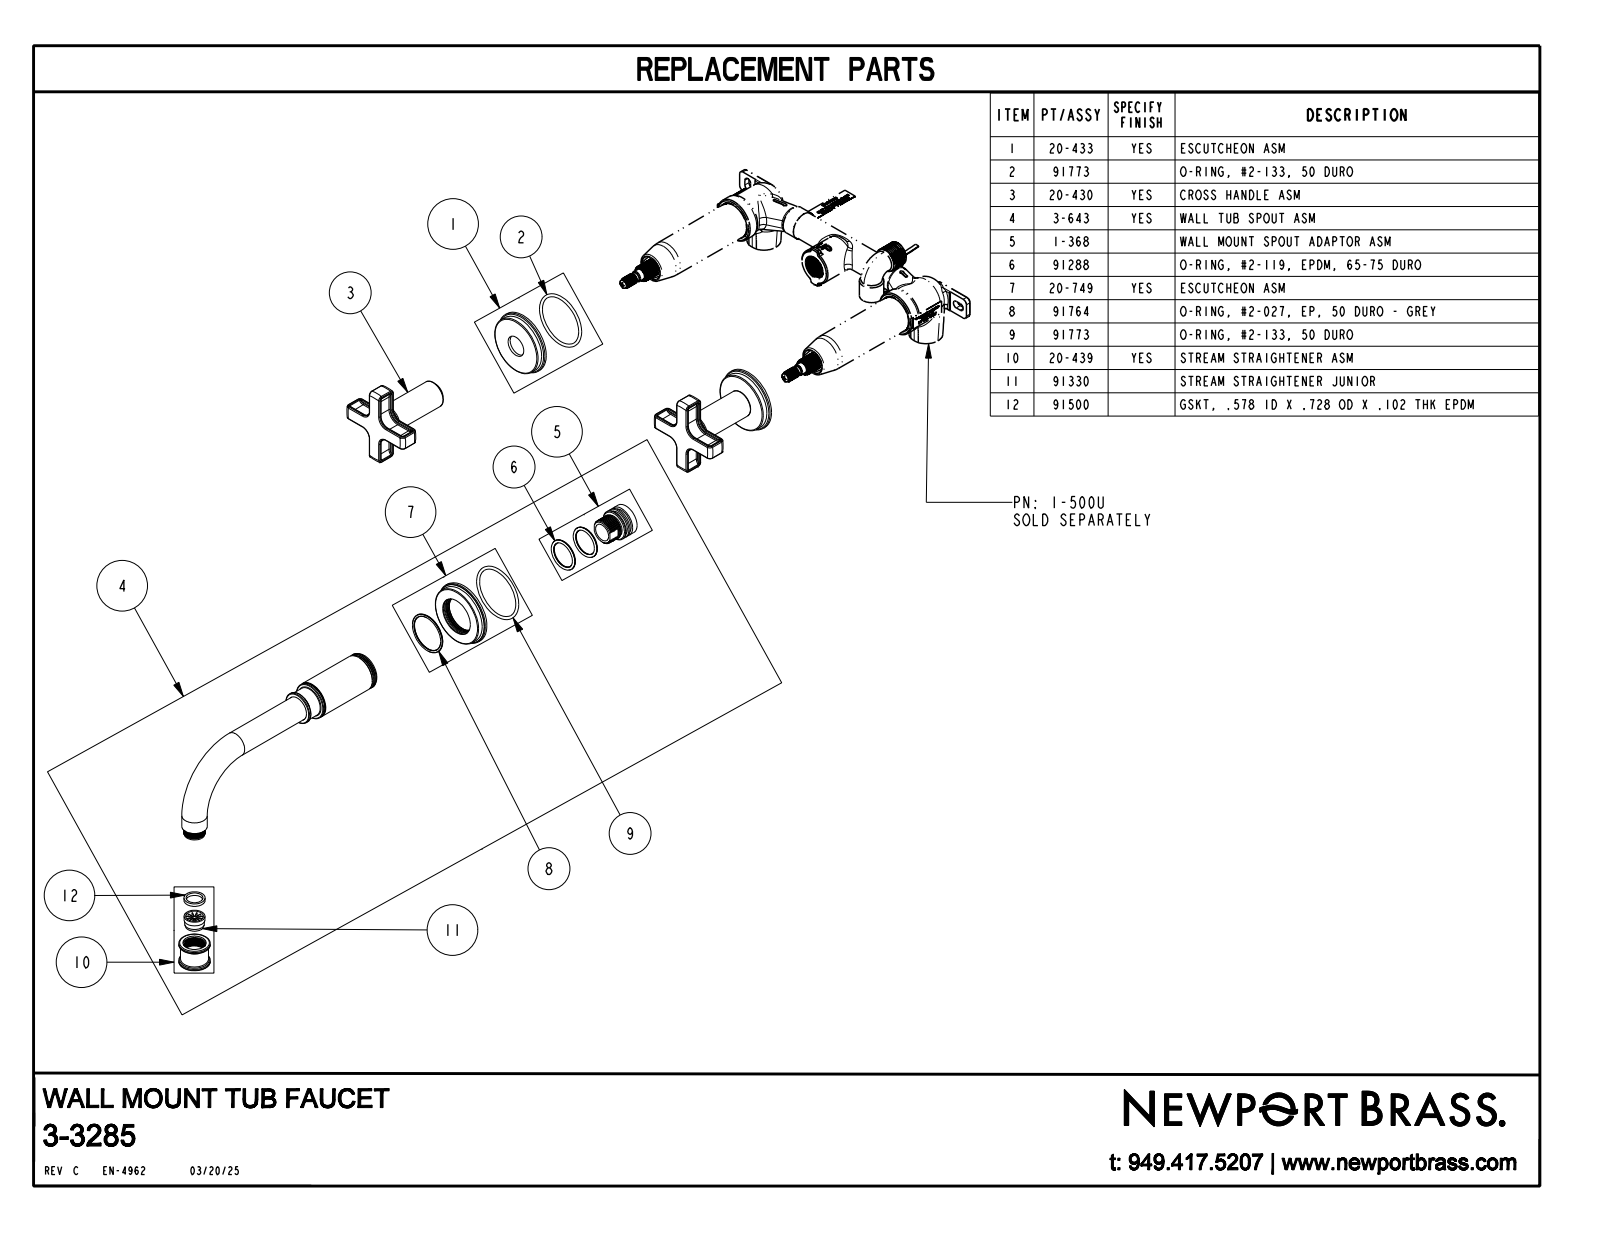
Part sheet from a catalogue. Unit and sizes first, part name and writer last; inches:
Units: inches
Overall size (bounding box): 10.675 × 10.66 × 8.79
Round bosses / shafts (diameter × count): ⌀2.25 ×3, ⌀2.09 ×3, ⌀0.975 ×2, ⌀0.875 ×2, ⌀0.85 ×2, ⌀0.5 ×2, ⌀1.312 ×1, ⌀1.14 ×1
Partial cylindrical surfaces — rounded edges, fillets, slot ends (radius × count): R0.03 ×68, R0.25 ×16, R0.325 ×8, R0.425 ×8, R1.4 ×2
Main face-to-face distances: 0.35, 3.251, 2.901, 2.551, 2.201, 0.7, 0.1, 0.3, 0.6, 0.4
Volume: 18.13 in³ · Surface area: 103.4 in²
Bodies: 3 solids, 508 faces (68 planar, 220 cylindrical, 220 other)
Part name (STEP PRODUCT): 3-3285_SW0001
STEP written by: CREO PARAMETRIC BY PTC INC, 2018400 (AUTOMOTIVE_DESIGN)
